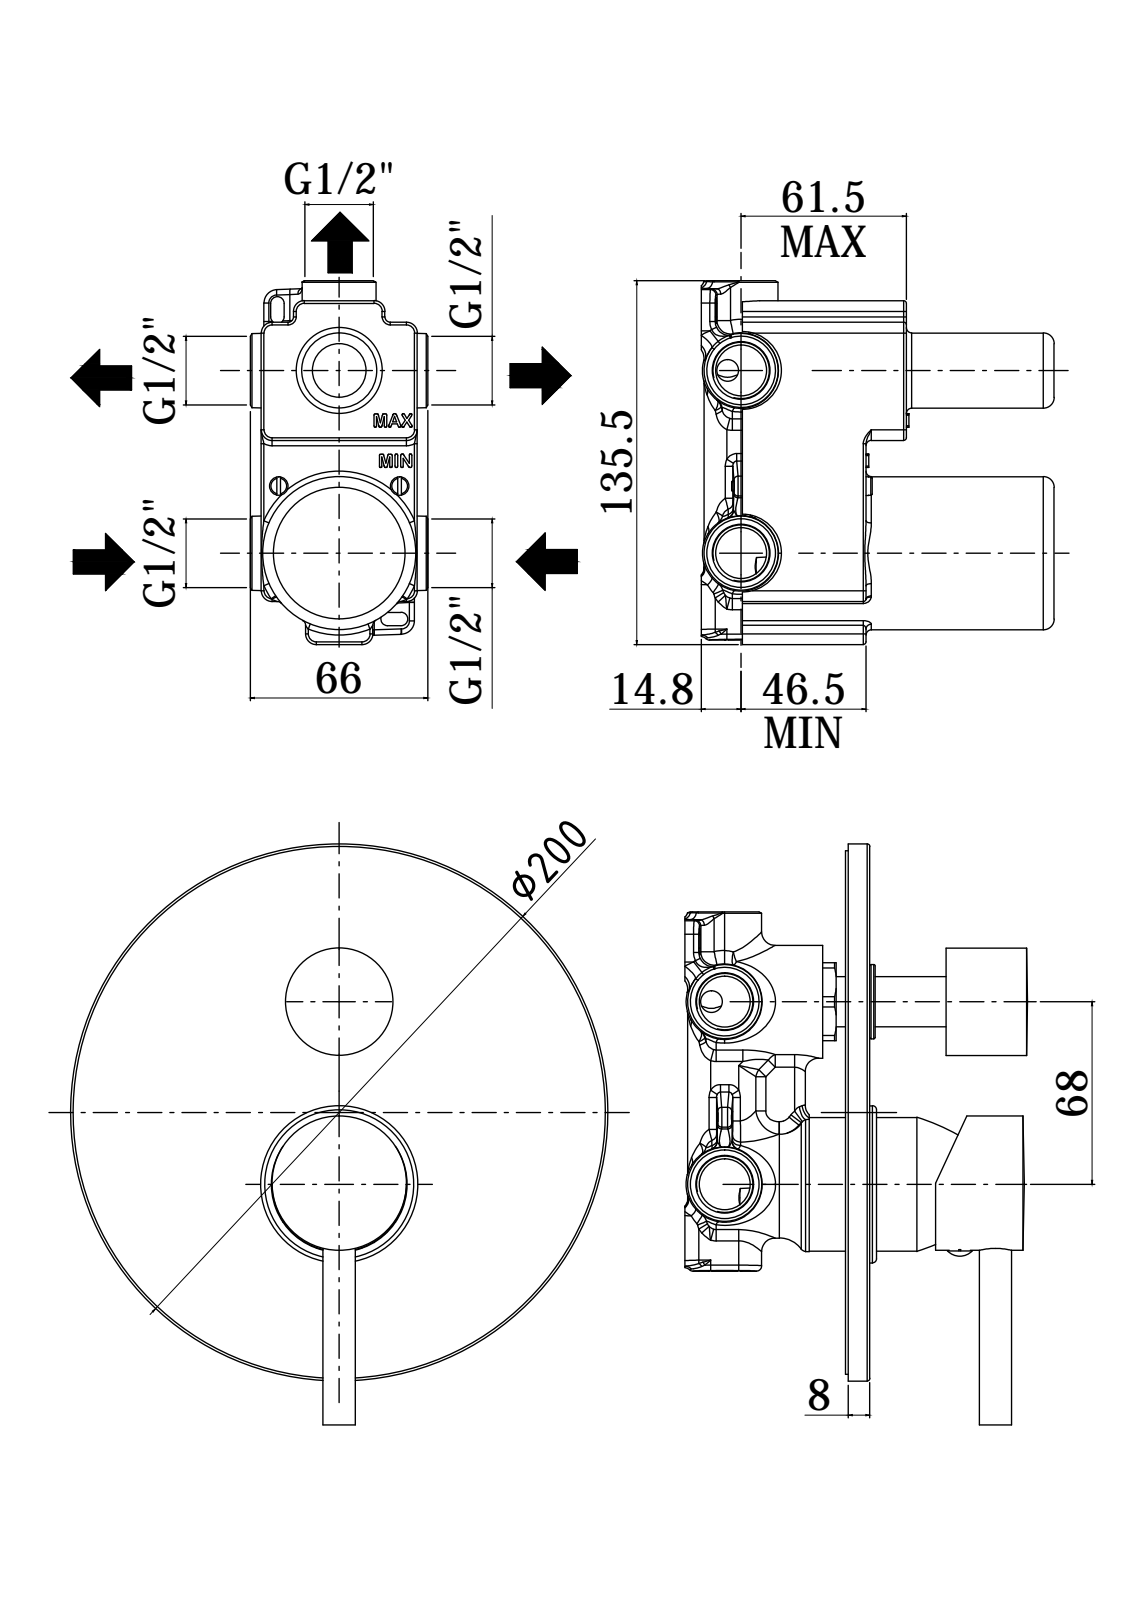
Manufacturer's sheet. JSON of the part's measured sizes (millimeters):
{"part_name": "BI018CR", "step_written_by": "CREO PARAMETRIC BY PTC INC, 2020044 (CONFIG_CONTROL_DESIGN)", "units": "millimeters", "bodies": {"solids": 4, "faces": 1061, "planar": 620, "cylindrical": 271, "other": 170}, "overall_size": [205.87, 200, 63.25], "volume_mm3": 222148, "surface_area_mm2": 142888, "round_holes": [[3.3, 3], [3, 2], [3.2, 1], [4, 1], [4.2, 1], [4.5, 1], [5, 1], [8, 1], [10, 1], [11, 1], [14, 1], [14.8, 1]], "round_bosses_or_shafts": [[200, 1], [195, 1], [58.5, 1], [54, 1], [50.3, 1], [44.8, 1], [43, 1], [40, 1]], "partial_cylinders_radius": [[0.2, 24], [0.5, 1], [3.85, 1], [6.5, 1], [7, 1], [10.05, 1], [11.9, 1], [12.3, 1]], "face_to_face_distances": [8, 7, 1, 10, 6.9, 9, 16.5, 39.9, 29.9, 55.8], "hole_center_spacings": [1.62, 7.1, 10, 13.8, 20.9, 26.75, 28.37, 41.25]}
